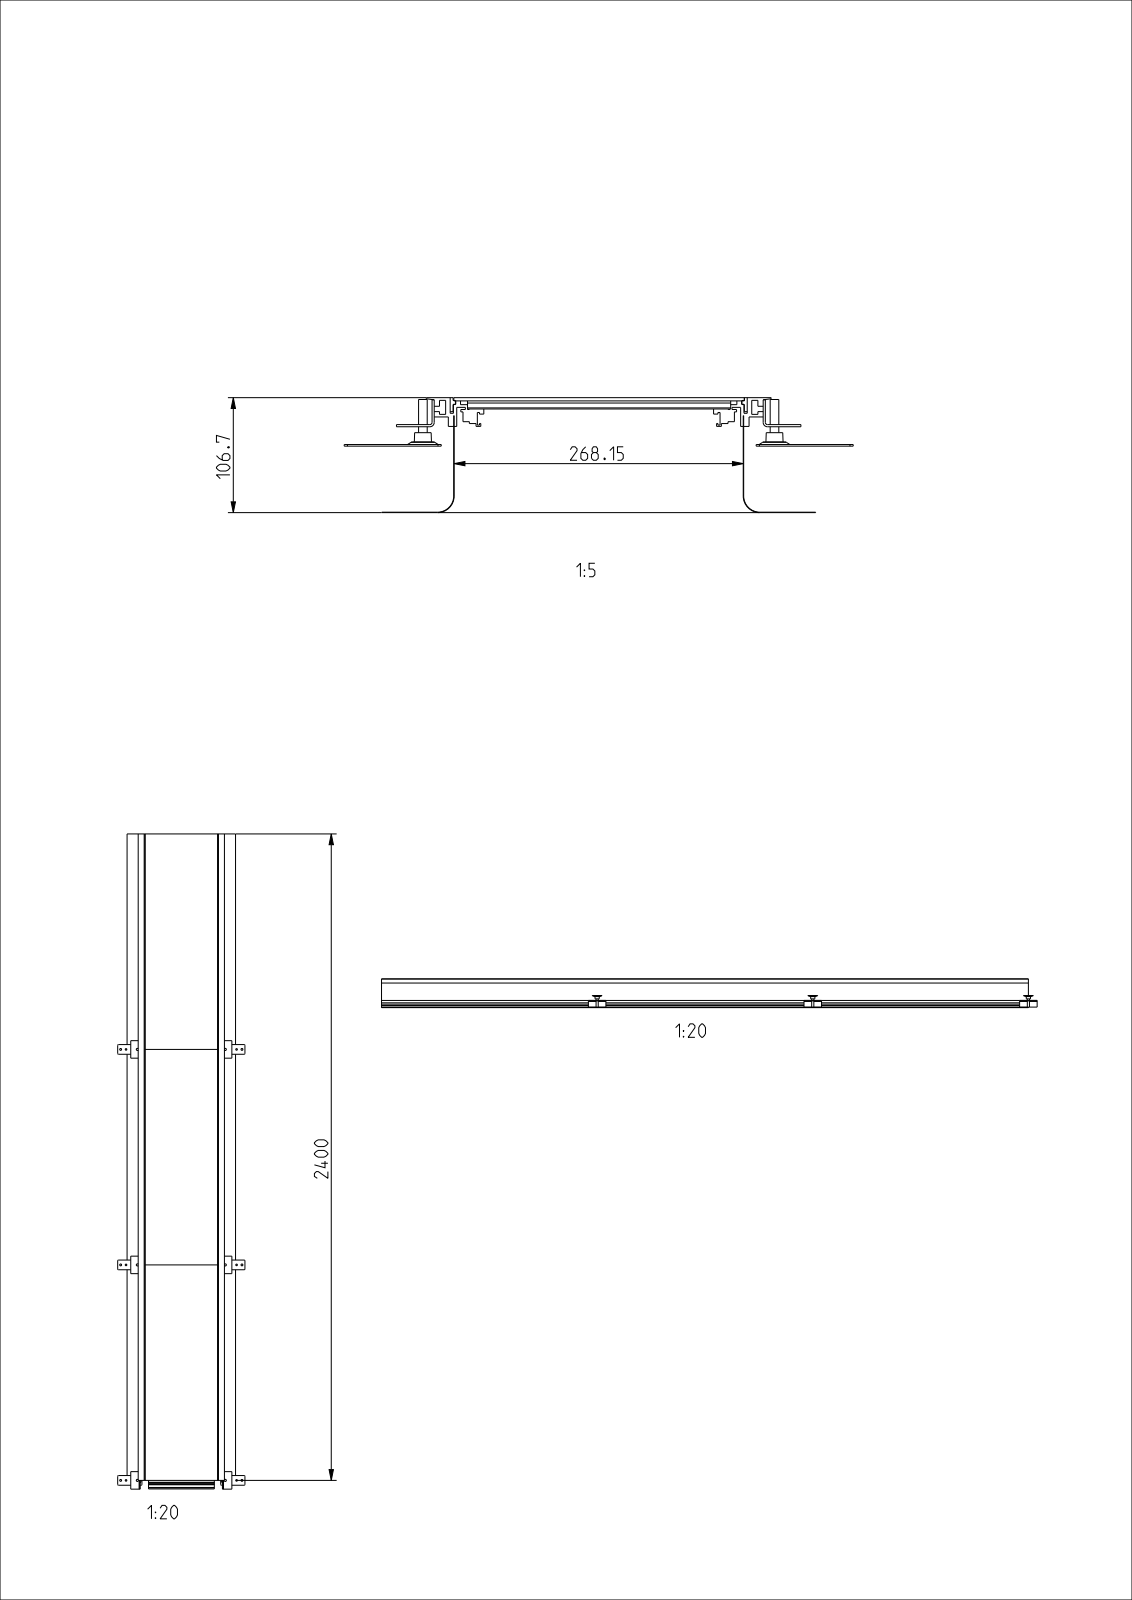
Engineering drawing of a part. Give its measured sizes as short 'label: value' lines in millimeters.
name: U05644KUN; U05650KUN; U05985KUN; U05347KUN (+8 more)
written by: CREO PARAMETRIC BY PTC INC, 2020281 (AUTOMOTIVE_DESIGN)
unit: mm
bodies: 41 solids, 720 faces (474 planar, 210 cylindrical, 36 other)
size: 2432.5 × 472.13 × 106.7
volume: 5 669 000 mm³; area: 4 686 000 mm²
holes: 6× ⌀6, 6× ⌀7, 6× ⌀8.5, 6× ⌀11.5, 6× ⌀17.5, 6× ⌀23
bosses: 6× ⌀20, 6× ⌀8
rounds: 62× R2, 24× R3, 14× R0.5, 2× R4, 2× R15, 2× R15.4
face distances: 3, 0.4, 268.55, 103.7, 106.7, 103.3, 106.3, 268.95, 268.15, 6.5
hole spacings: 800, 800.25, 801.1, 802.4, 880.64, 889.18, 908.3, 20
